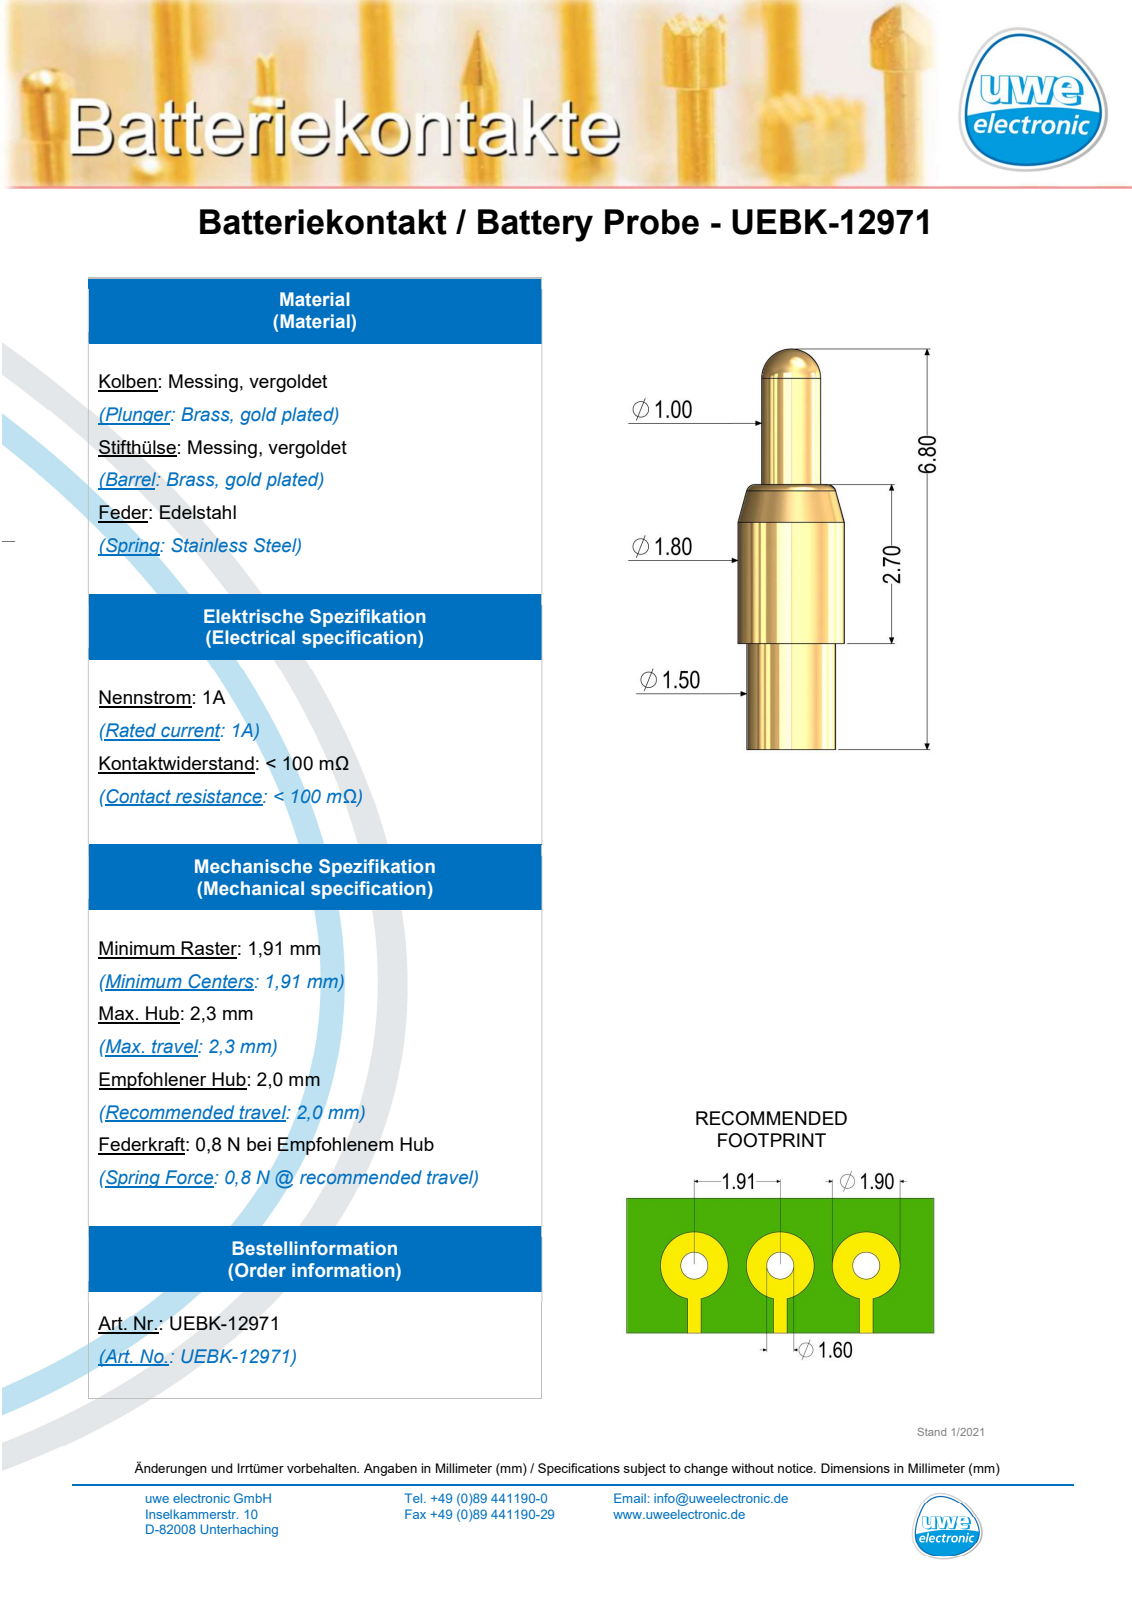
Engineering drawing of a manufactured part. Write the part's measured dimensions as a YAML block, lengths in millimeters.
part_name: "UEBK-12971_2017_08_28"
step_written_by: "SolidWorks 2017 (AUTOMOTIVE_DESIGN)"
units: millimeters
bodies: {solids: 1, faces: 15, planar: 3, cylindrical: 6, other: 6}
overall_size: [6.8, 1.8, 1.8]
volume: 11
surface_area: 34
round_bosses_or_shafts:
  - {diameter: 1.8, count: 1}
  - {diameter: 1.5, count: 1}
  - {diameter: 1, count: 1}
face_to_face_distances: [1.8, 2.7, 4.5]
